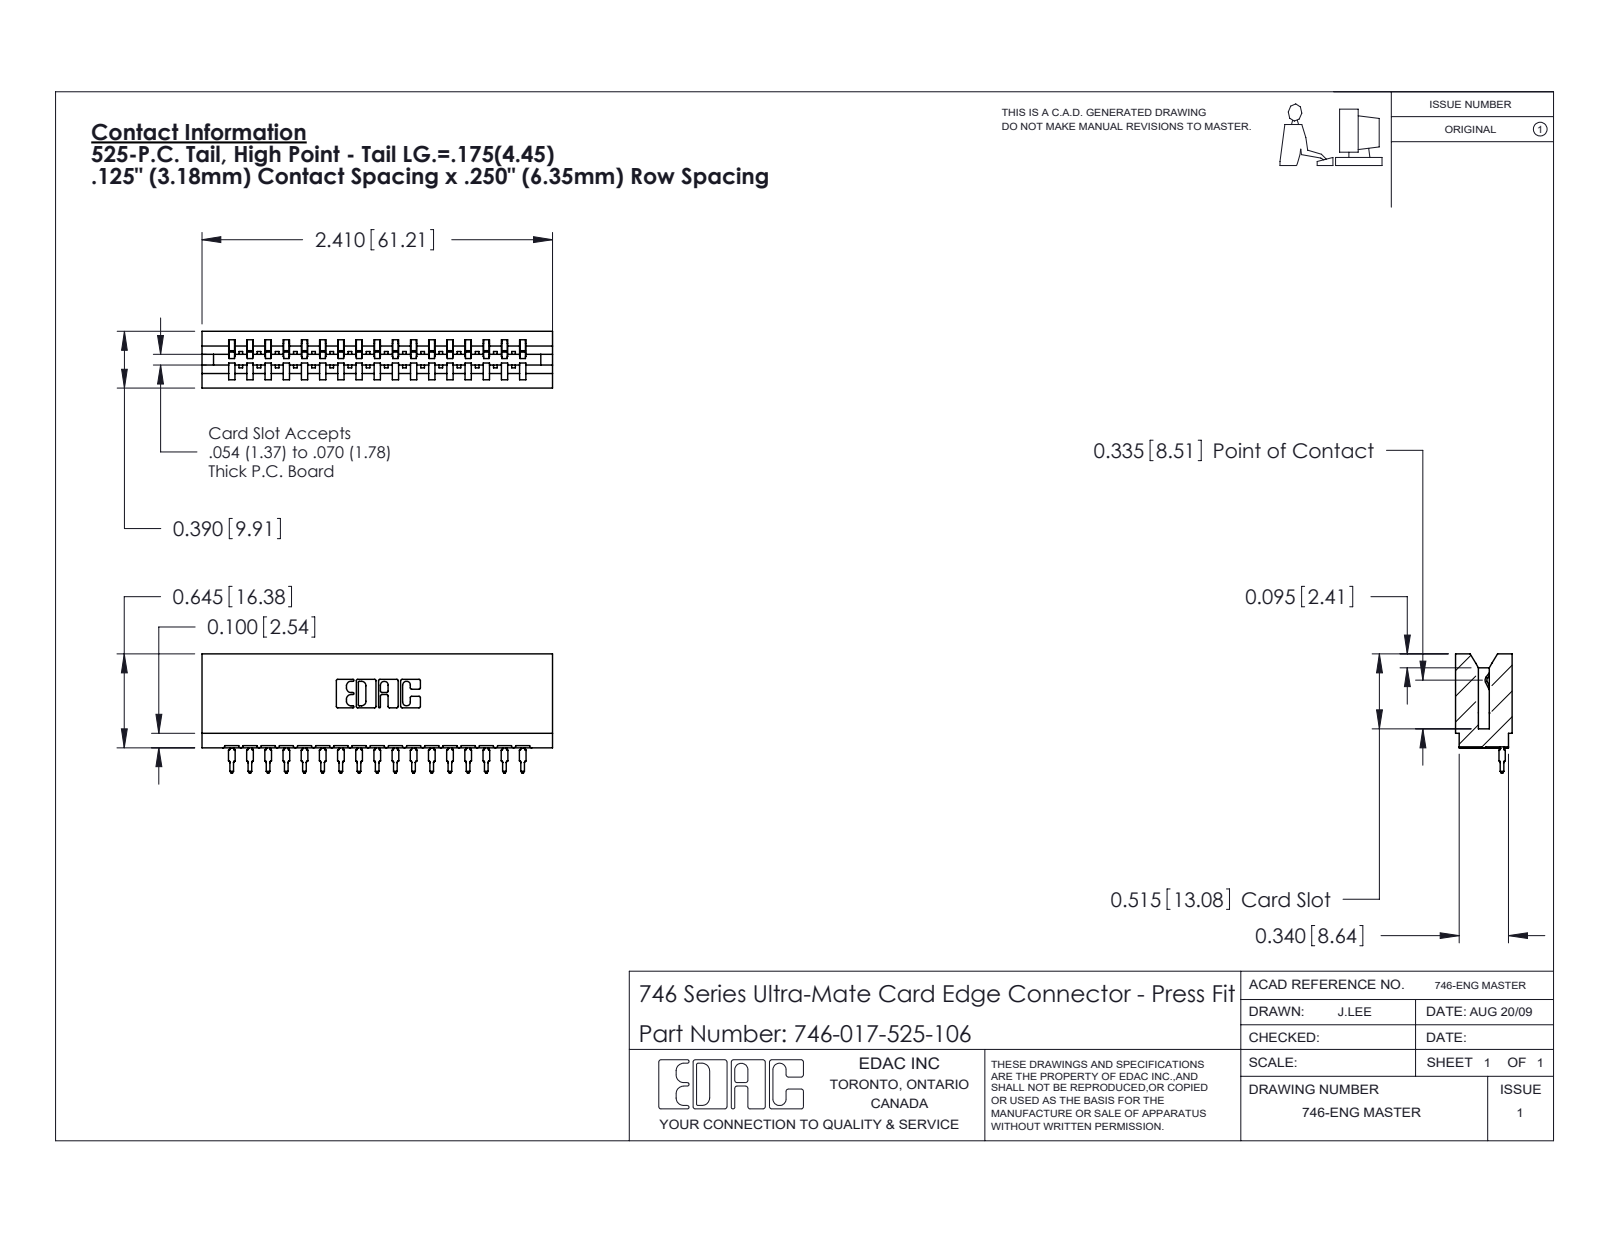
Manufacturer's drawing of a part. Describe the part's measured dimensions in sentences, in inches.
The part is named "746-292-001_525; 746 Part_.515 Slot Depth - 06; 746-017-525-106". Its 3-D file was written by "SolidWorks 2020 (CONFIG_CONTROL_DESIGN)". It is 18 solids with 1934 faces: 1127 planar, 365 cylindrical and 442 other. Overall it measures 2.41 by 0.819 by 0.39 inches. Its volume is 0.398 cubic inches and its surface area 14.23 square inches. Partial cylindrical surfaces (rounded edges, fillets, slot ends): 34 of radius 0.021, 22 of radius 0.01, 18 of radius 0.015, 6 of radius 0.007, 6 of radius 0.031, 4 of radius 0.005, 4 of radius 0.011, 3 of radius 0.026. The main face-to-face distances are 0.25, 0.057, 0.333, 0.39, 0.5, 0.125, 0.125, 0.025, 0.292, 0.375.
